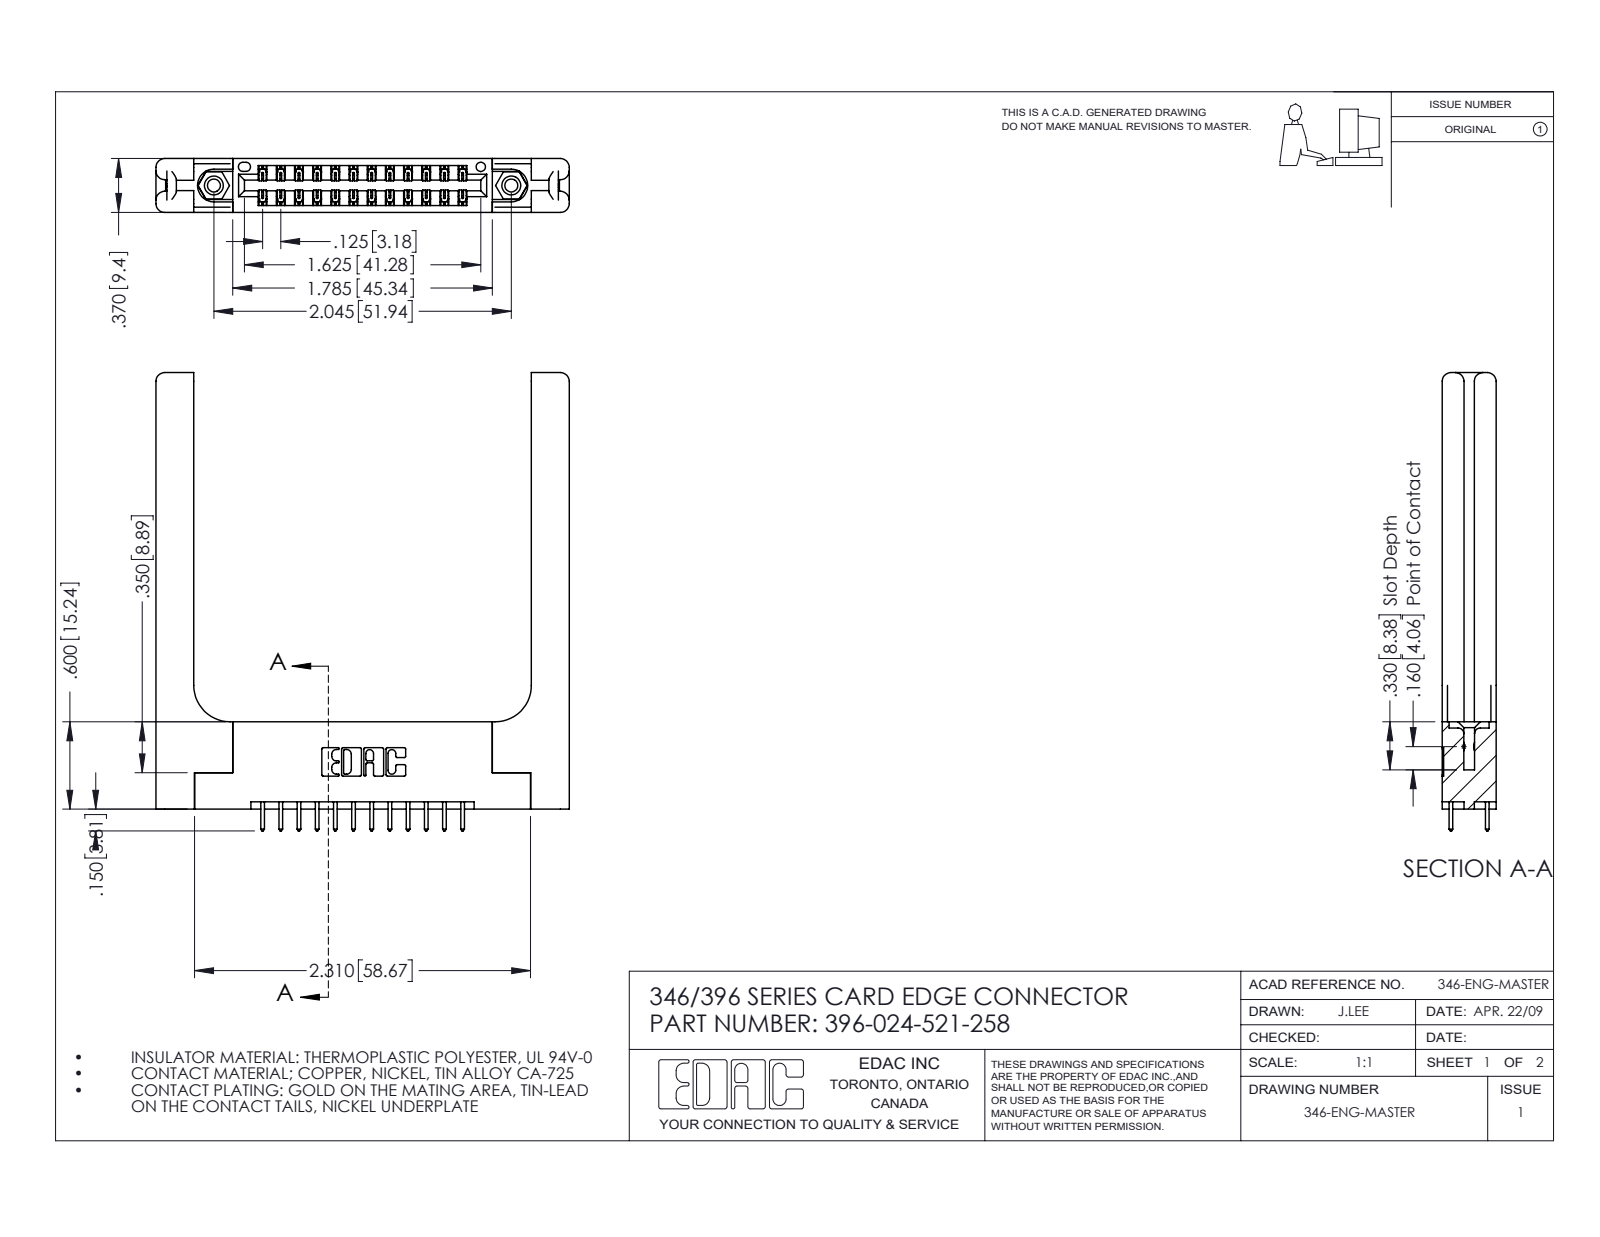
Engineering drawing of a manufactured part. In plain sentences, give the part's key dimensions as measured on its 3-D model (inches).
The part is named "346 Part_Flush Mounting Lugs - 0.156 Dia-TH; 346-220-058_345-220-058; 345-250-001_345-250-001-102; 345-292-001_345-293-121 (+1 more)". Its 3-D file was written by "SolidWorks 2016 (CONFIG_CONTROL_DESIGN)". It is 29 solids with 1626 faces: 1064 planar, 502 cylindrical and 60 other. Overall it measures 3.15 by 2.841 by 0.37 inches. Its volume is 0.872 cubic inches and its surface area 21.35 square inches. Round holes: 2 of diameter 0.089, 2 of diameter 0.125, 2 of diameter 0.156, 1 of diameter 0.064. Round bosses or shafts: 2 of diameter 0.155. Partial cylindrical surfaces (rounded edges, fillets, slot ends): 36 of radius 0.006, 24 of radius 0.01, 22 of radius 0.01, 16 of radius 0.06, 6 of radius 0.007, 6 of radius 0.031, 3 of radius 0.026, 2 of radius 0.014. The main face-to-face distances are 0.37, 0.15, 0.072, 0.148, 0.048, 0.322, 0.25, 0.102, 0.22, 0.173. The hole center spacings are 0.246, 1.839, 2.045.
